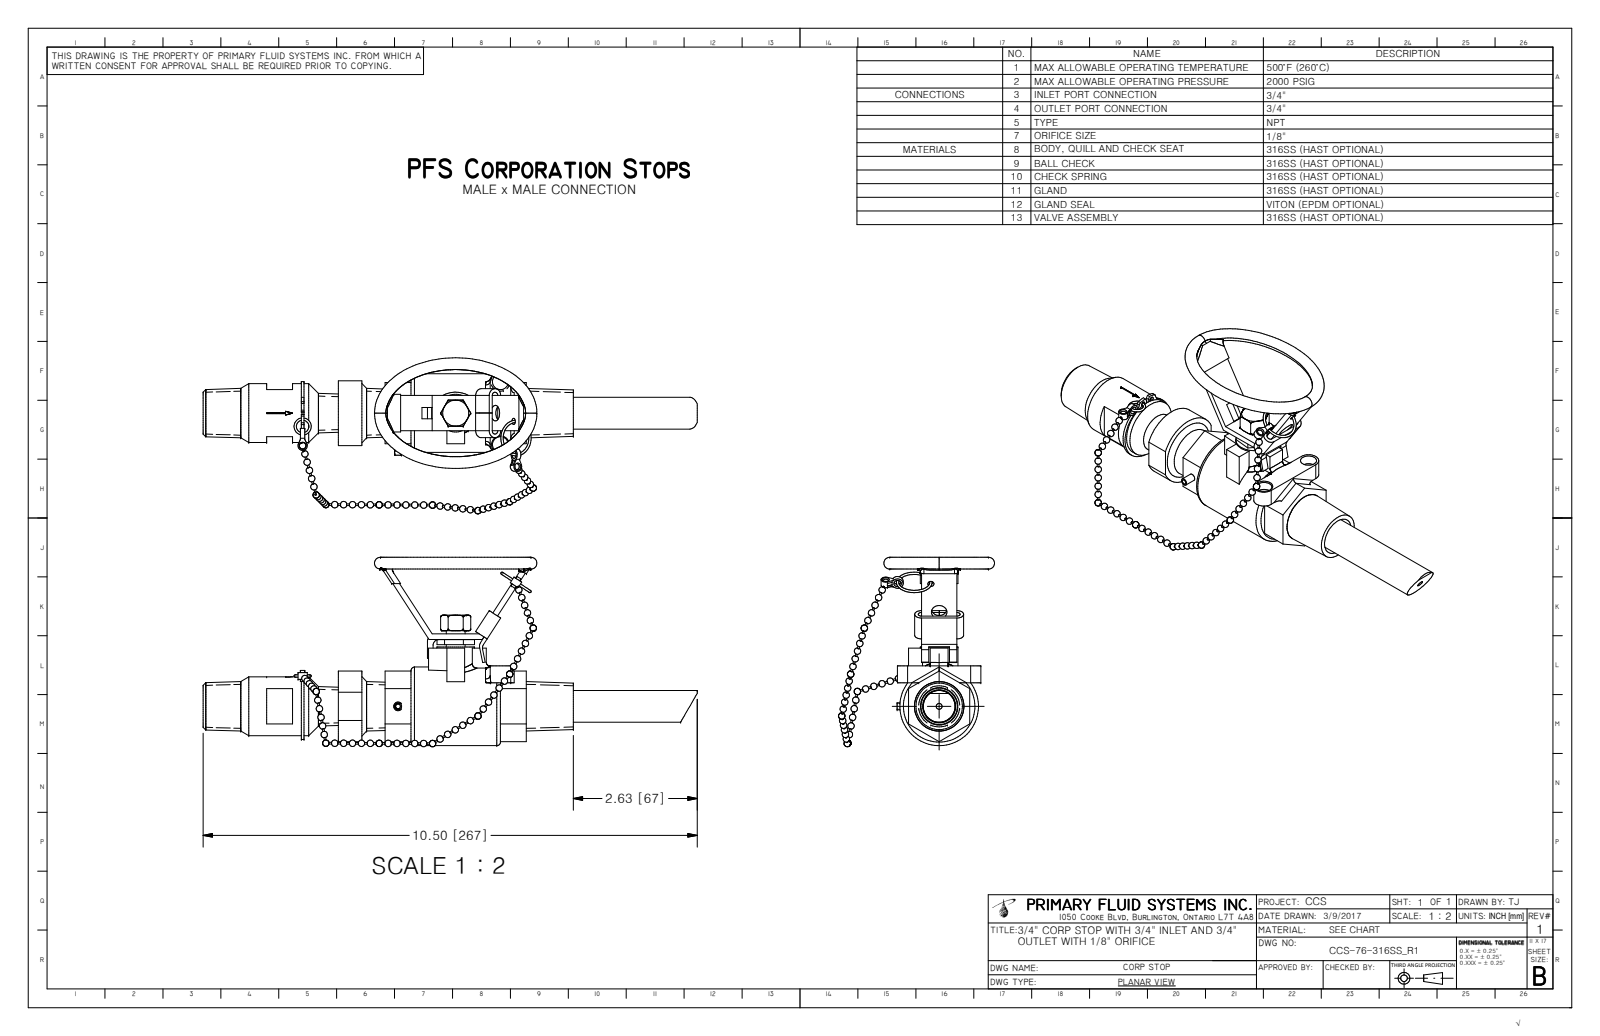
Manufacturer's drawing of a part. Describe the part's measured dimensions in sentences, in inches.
The part is named "CCS-76-316SS_R0". Its 3-D file was written by "Autodesk Inventor 2009 (AUTOMOTIVE_DESIGN)". It is 0 solids with 393 faces: 178 planar, 42 cylindrical and 173 other. Overall it measures 10.5 by 4.024 by 3.314 inches. Round holes: 1 of diameter 0.098, 1 of diameter 0.125, 1 of diameter 0.25, 1 of diameter 0.469. Round bosses or shafts: 1 of diameter 1.67, 1 of diameter 1.343, 1 of diameter 1.25, 1 of diameter 0.8, 1 of diameter 0.675, 1 of diameter 0.4, 1 of diameter 0.15. Partial cylindrical surfaces (rounded edges, fillets, slot ends): 4 of radius 0.075, 2 of radius 0.05, 2 of radius 0.054, 2 of radius 0.145, 2 of radius 0.15, 2 of radius 0.197, 1 of radius 0.125, 1 of radius 0.165. The main face-to-face distances are 1.299, 0.12, 1, 0.15, 1.15, 0.55, 0.275, 1.025, 0.125, 0.12. The hole center spacings are 0.657.
